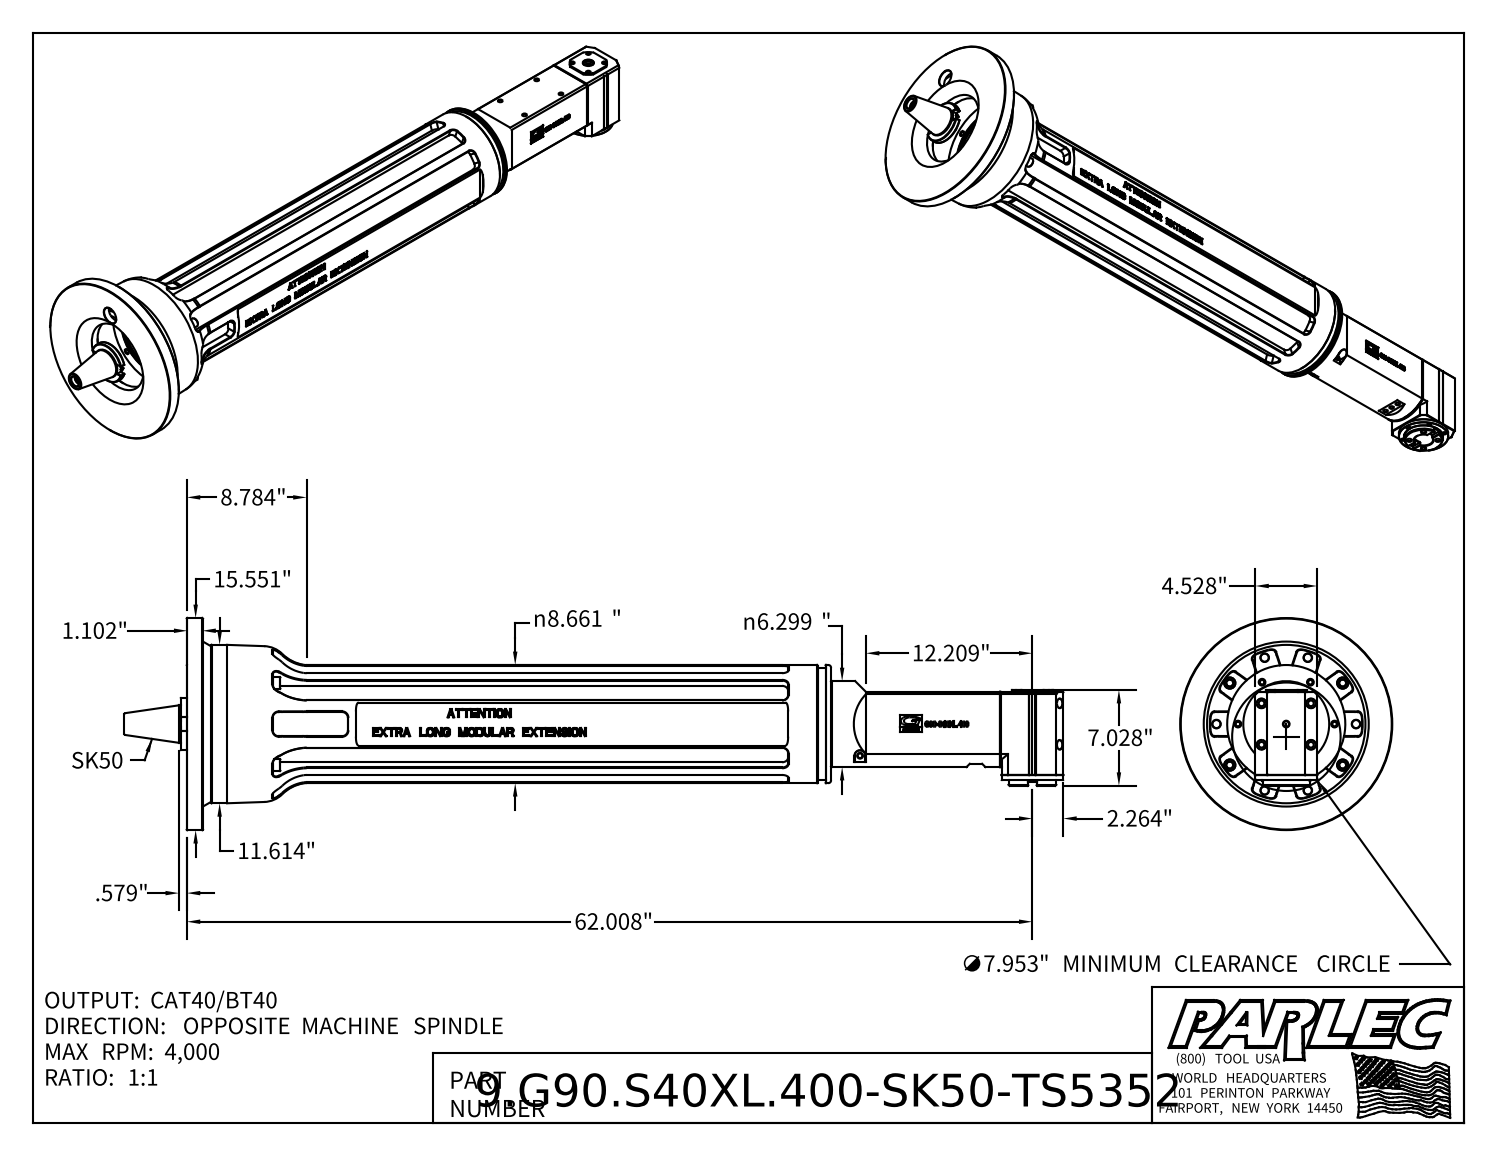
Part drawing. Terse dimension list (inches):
name: 9.G90.S40XL.400-SK50-TS5352; T0000527373
written by: Autodesk Inventor 2022 (AUTOMOTIVE_DESIGN)
unit: in
bodies: 4 solids, 3290 faces (2152 planar, 357 cylindrical, 781 other)
size: 68.858 × 15.551 × 15.551
volume: 2 075 in³; area: 4 150 in²
holes: 14× ⌀0.197, 14× ⌀0.268, 13× ⌀0.551, 12× ⌀0.354, 11× ⌀0.335, 11× ⌀0.591, 10× ⌀0.165, 10× ⌀0.217, 10× ⌀0.413, 9× ⌀0.402, 8× ⌀0.346, 5× ⌀0.669
bosses: 4× ⌀0.827, 4× ⌀0.551, 1× ⌀15.551, 1× ⌀11.614, 1× ⌀9.528, 1× ⌀9.134, 1× ⌀8.661, 1× ⌀8.268
rounds: 36× R0.433, 20× R0.118, 7× R0.394, 4× R0.197, 2× R0.236, 2× R0.295, 1× R0.184, 1× R0.242
face distances: 1.772, 7.086, 7.087, 1.77, 6.298, 1.772, 8.069, 0.591, 1.181, 4.528
hole spacings: 1.969, 2.362, 5.118, 8.281, 2.983, 7.202, 9.735, 3.937
